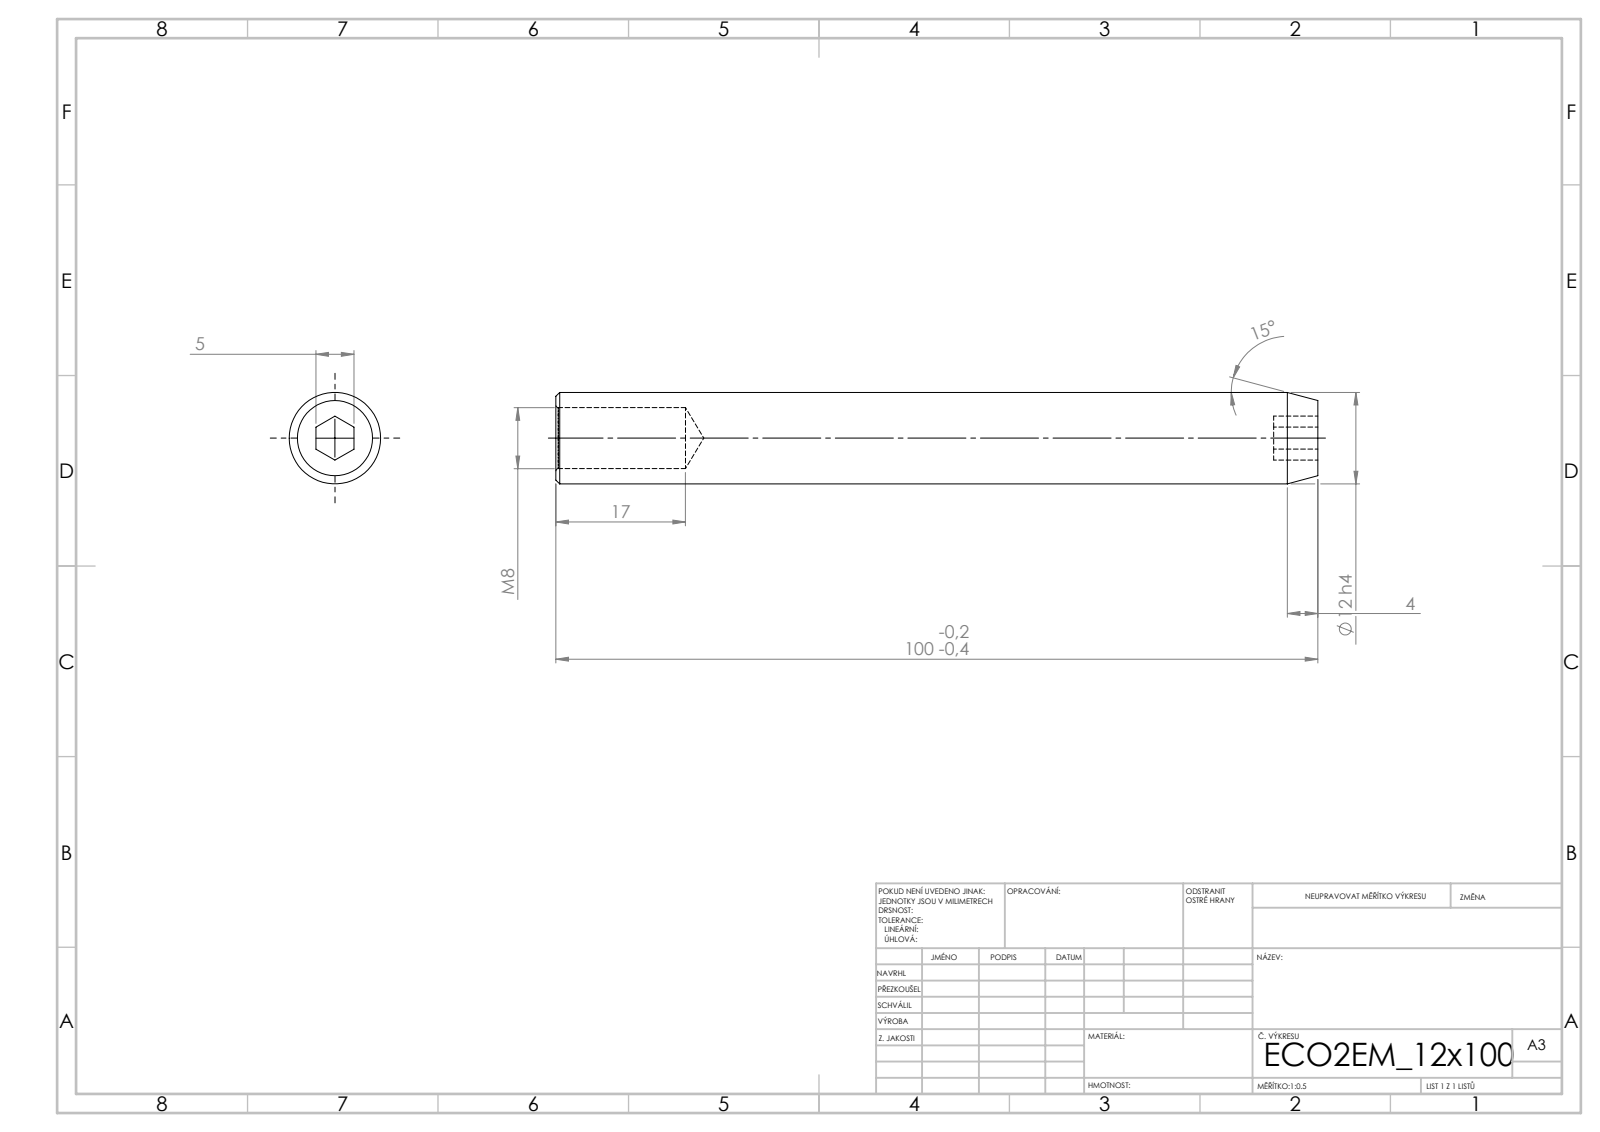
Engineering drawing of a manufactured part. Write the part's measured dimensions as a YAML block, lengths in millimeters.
step_written_by: "SolidWorks 2019 (CONFIG_CONTROL_DESIGN)"
units: millimeters
bodies: {solids: 1, faces: 21, planar: 9, cylindrical: 4, other: 8}
overall_size: [100, 12, 12]
volume: 10208
surface_area: 4472
round_holes:
  - {diameter: 8, count: 1}
round_bosses_or_shafts:
  - {diameter: 12, count: 1}
face_to_face_distances: [5, 100, 5.8, 94.2]
